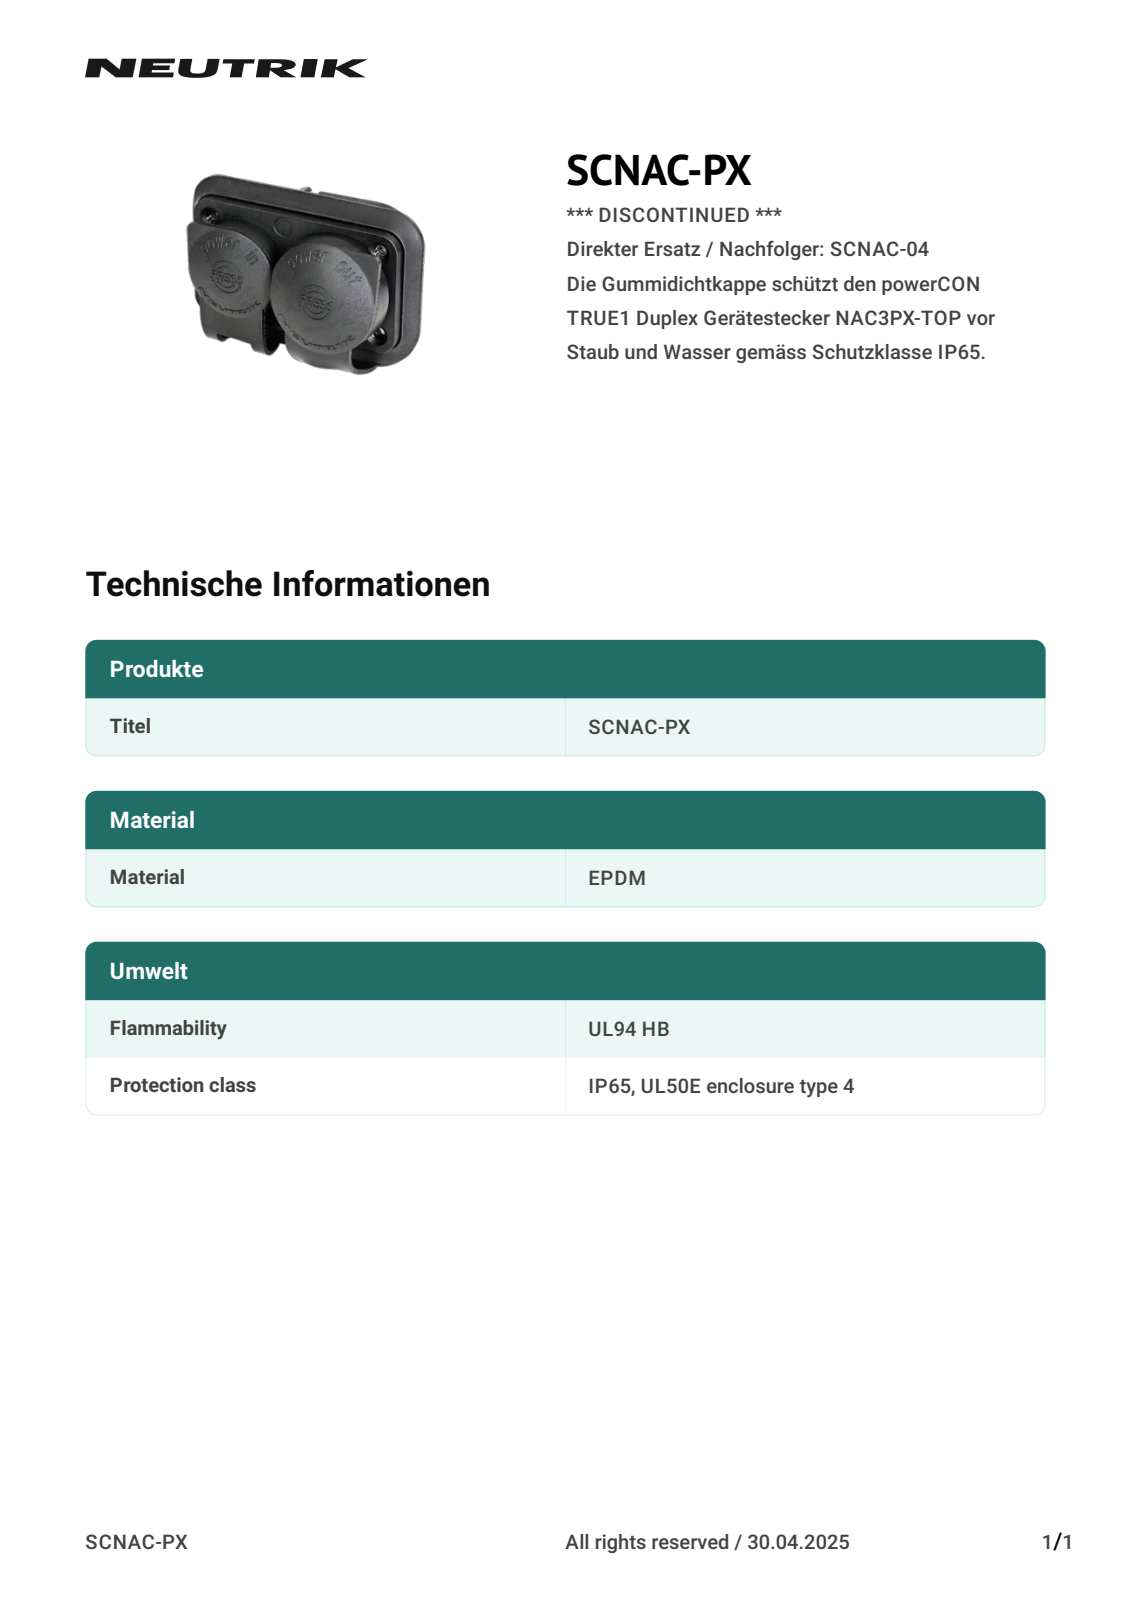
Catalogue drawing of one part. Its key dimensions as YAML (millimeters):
part_name: "91220861_AF0; 30009915_ASM"
step_written_by: "CREO PARAMETRIC BY PTC INC, 2021184 (AUTOMOTIVE_DESIGN)"
units: millimeters
bodies: {solids: 1, faces: 1211, planar: 854, cylindrical: 80, other: 277}
overall_size: [91.2, 69.2, 12.2]
volume: 6217
surface_area: 11000
round_holes:
  - {diameter: 3.5, count: 4}
  - {diameter: 24, count: 1}
  - {diameter: 29.2, count: 1}
round_bosses_or_shafts:
  - {diameter: 30.8, count: 1}
  - {diameter: 26, count: 1}
partial_cylinders:
  - {radius: 1, count: 8}
  - {radius: 0.5, count: 6}
  - {radius: 0.2, count: 4}
  - {radius: 0.3, count: 4}
  - {radius: 0.74, count: 4}
  - {radius: 5, count: 4}
  - {radius: 5.7, count: 4}
  - {radius: 6.2, count: 4}
face_to_face_distances: [2, 0.8, 1.2, 3, 1, 1.8, 4, 4.2, 4.9, 3.4]
hole_center_spacings: [24.4, 50, 55.64, 28.91, 42.35, 43.2, 57.21, 57.24]
